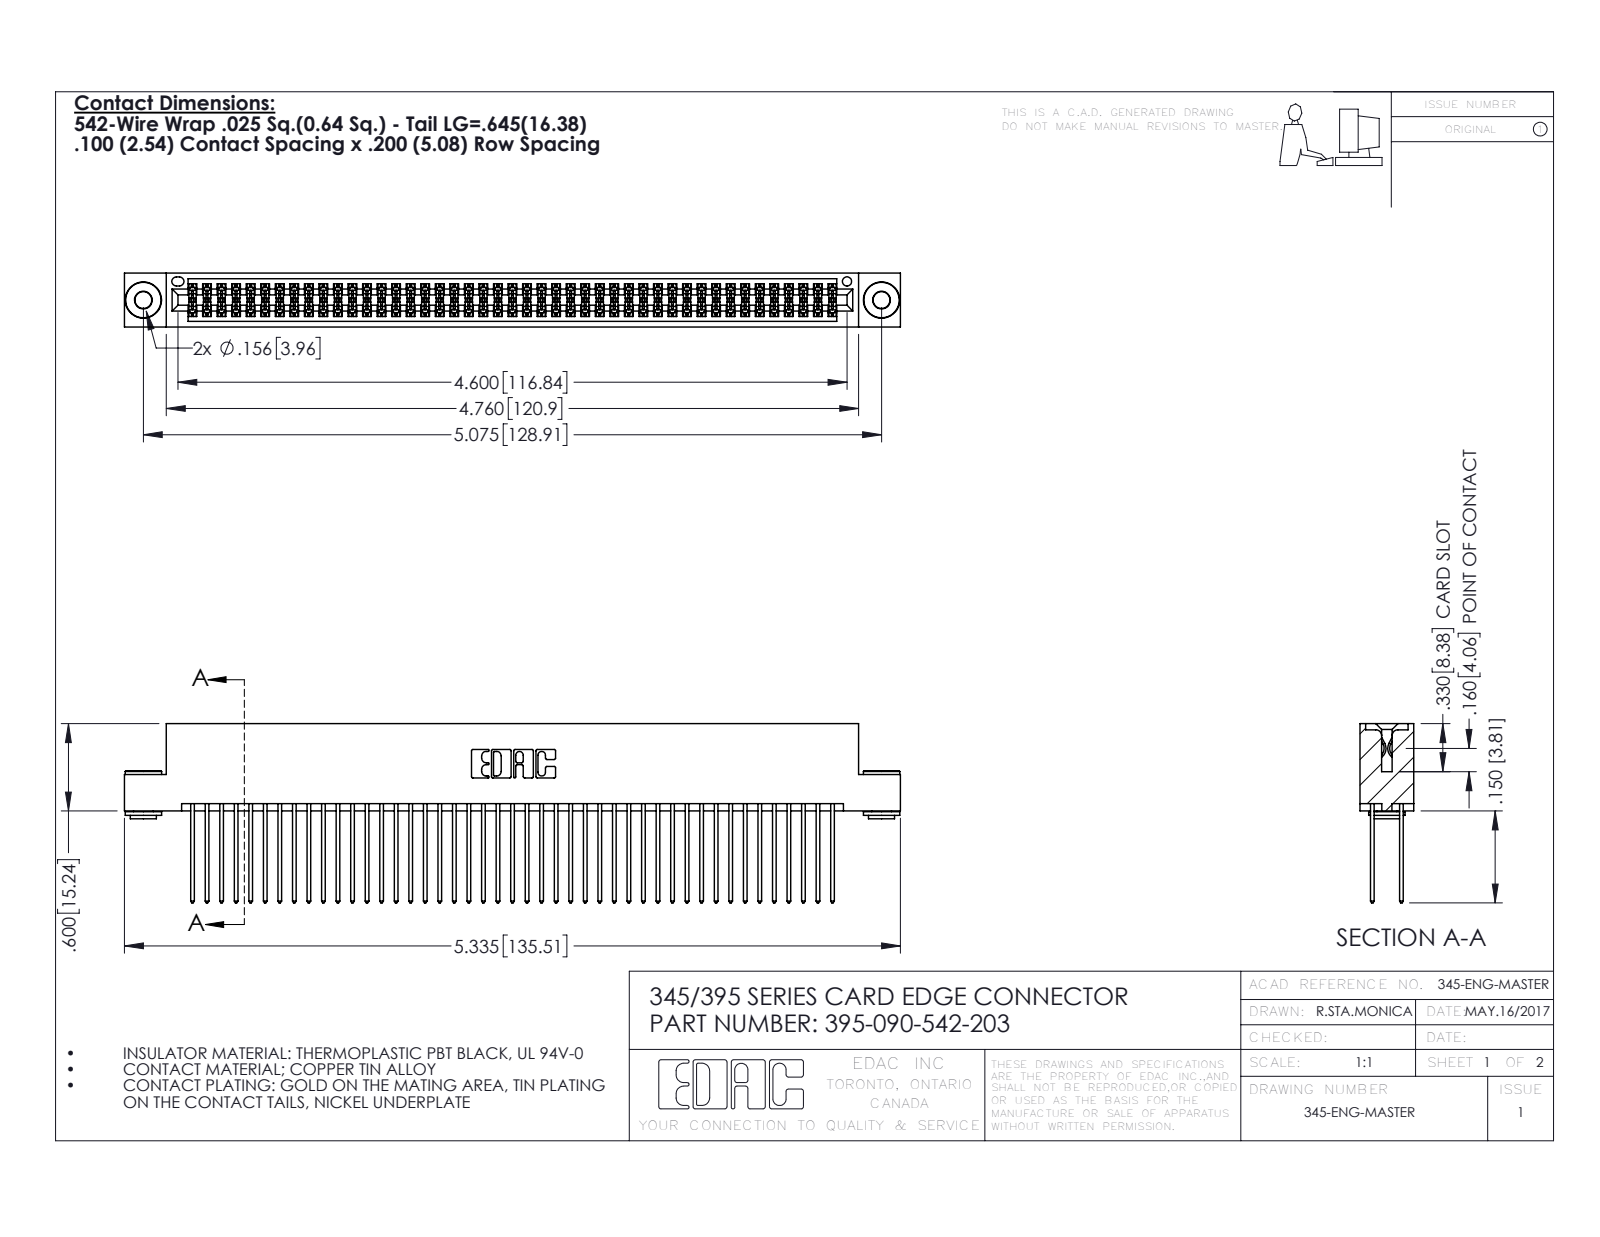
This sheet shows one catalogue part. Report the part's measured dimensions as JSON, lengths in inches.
{"part_name": "395-090-542-203; 345-292-001_345-293-142; 345-250-002_345-250-002-102; 345 Part_Flush Mounting Lugs - 0.156 Dia-TH", "step_written_by": "SolidWorks 2016 (CONFIG_CONTROL_DESIGN)", "units": "inches", "bodies": {"solids": 93, "faces": 4664, "planar": 3060, "cylindrical": 1596, "other": 8}, "overall_size": [5.335, 1.232, 0.37], "volume_in3": 0.832, "surface_area_in2": 34.68, "round_holes": [[0.116, 2], [0.156, 2], [0.064, 1]], "round_bosses_or_shafts": [[0.25, 2], [0.18, 2], [0.136, 2]], "partial_cylinders_radius": [[0.006, 135], [0.01, 90], [0.01, 22], [0.007, 6], [0.031, 6], [0.026, 3], [0.014, 2], [0.019, 2]], "face_to_face_distances": [0.072, 0.298, 0.2, 0.025, 0.098, 0.272, 0.225, 0.37, 0.175, 0.149], "hole_center_spacings": [0.27, 4.839, 5.075]}
